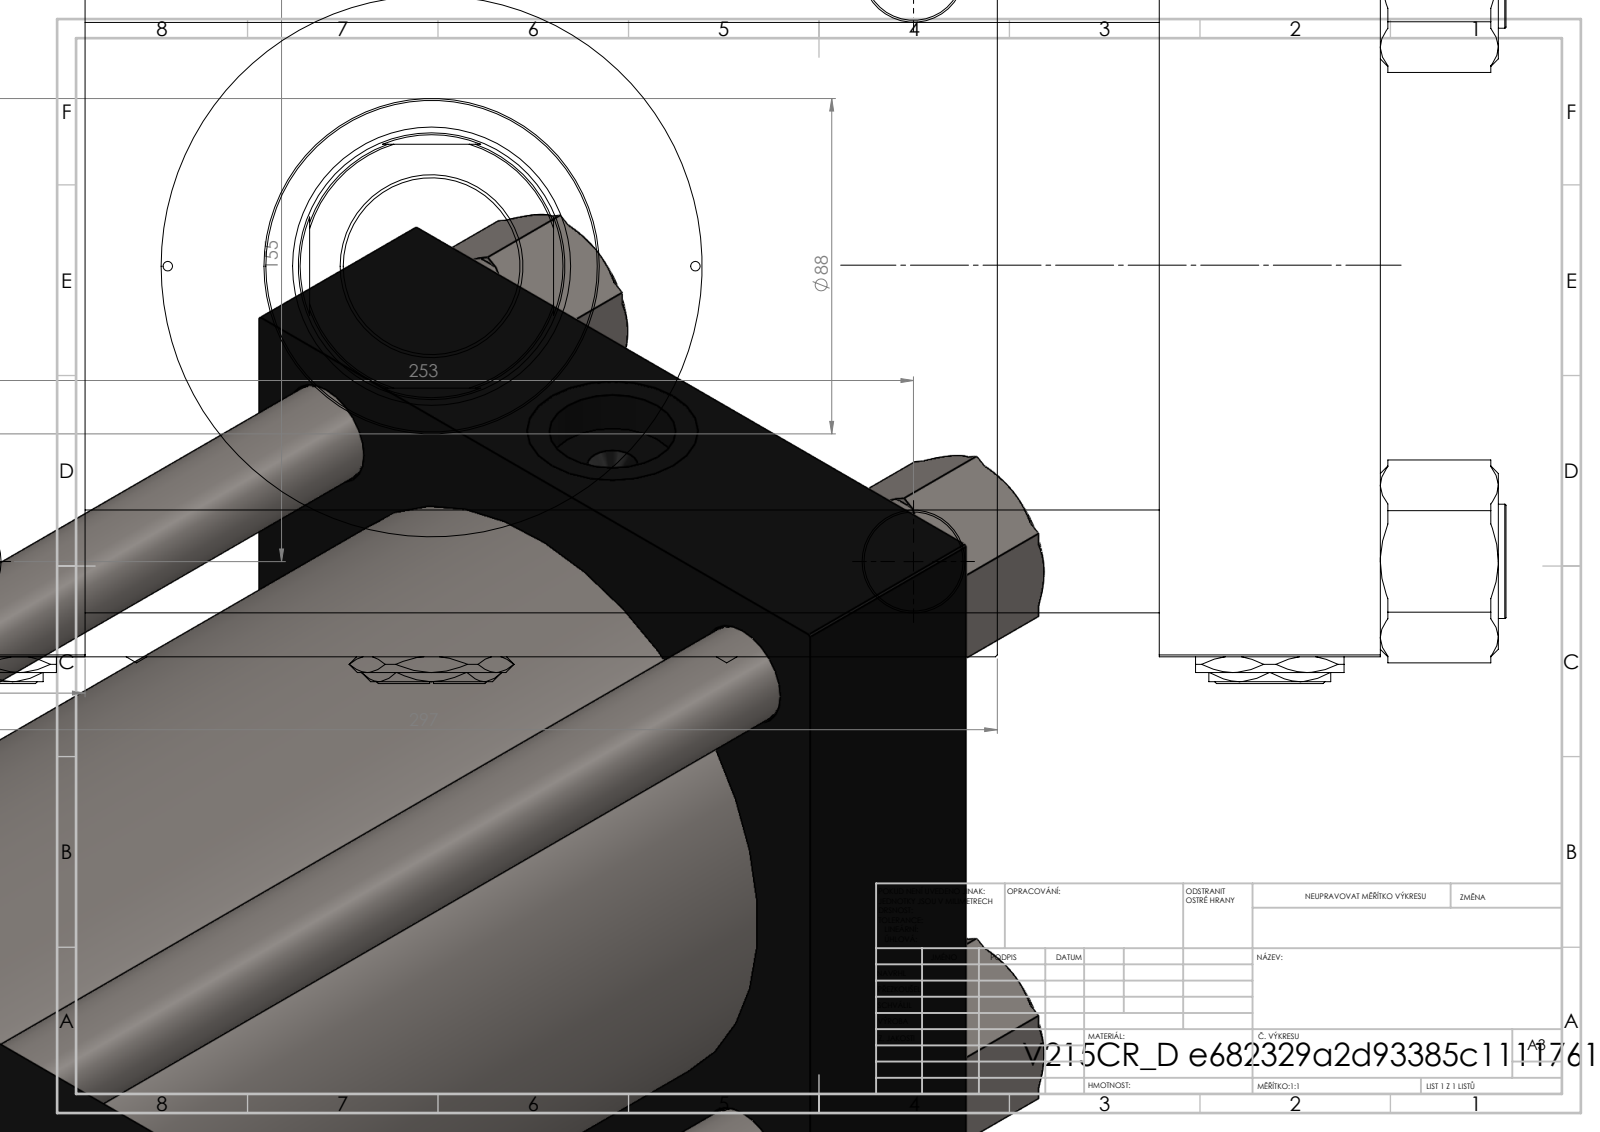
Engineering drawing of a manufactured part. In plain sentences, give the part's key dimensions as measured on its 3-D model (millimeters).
The part is named "ROD_END_AH; Zatka_pro_OIL_PORT; V215CR_D_TYCINKA; V215CR_VCP_D (+3 more)". Its 3-D file was written by "SolidWorks 2019 (CONFIG_CONTROL_DESIGN)". It is 14 solids with 1270 faces: 598 planar, 106 cylindrical and 566 other. Overall it measures 549 by 297 by 213.57 millimeters. Its volume is 9 434 000 cubic millimeters and its surface area 1 051 000 square millimeters. Round holes: 4 of diameter 26, 4 of diameter 27, 2 of diameter 2.5, 2 of diameter 7, 2 of diameter 33.24, 2 of diameter 45, 1 of diameter 46.5, 1 of diameter 70, 1 of diameter 73, 1 of diameter 120, 1 of diameter 142, 1 of diameter 160. Round bosses or shafts: 4 of diameter 30, 1 of diameter 166, 1 of diameter 88, 1 of diameter 48, 1 of diameter 46. Partial cylindrical surfaces (rounded edges, fillets, slot ends): 1 of radius 34. The main face-to-face distances are 58, 340, 282, 396, 338, 56, 205, 46, 251, 72. The hole center spacings are 49.05, 77.88, 96.35, 109.53, 148.35, 154.9, 162.53, 165.89.
